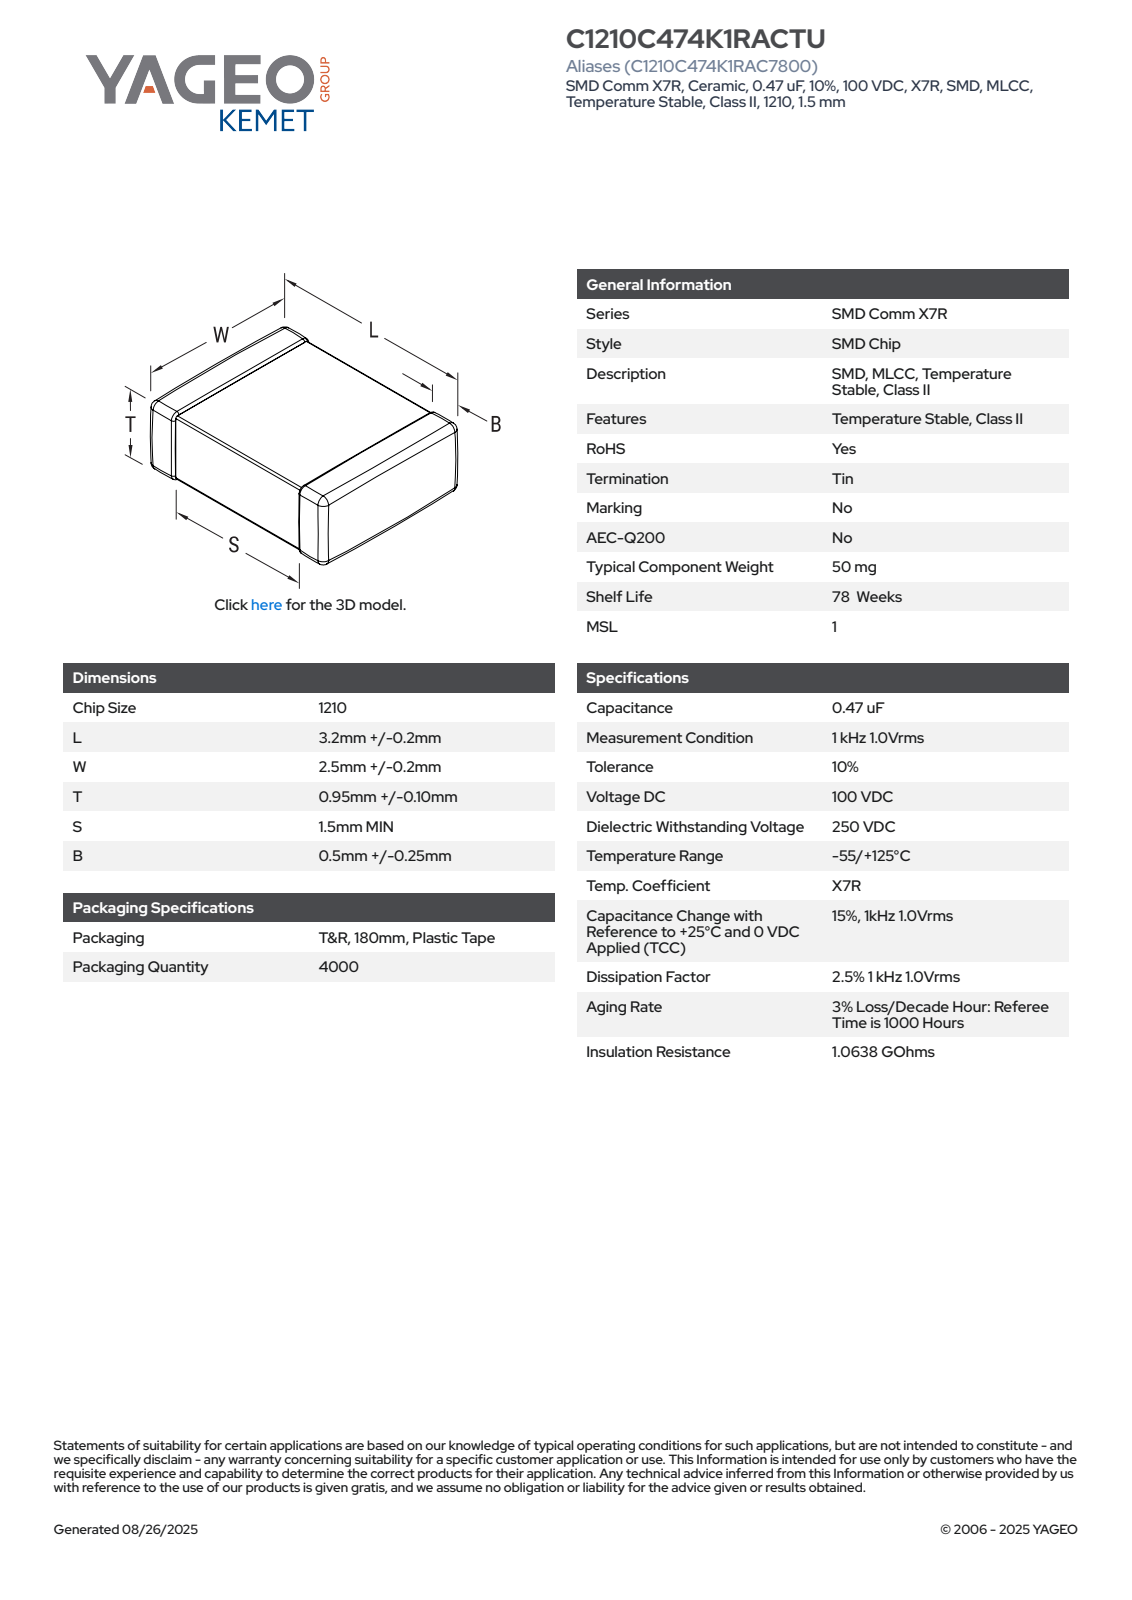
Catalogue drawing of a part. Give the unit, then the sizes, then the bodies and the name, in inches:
Units: inches
Overall size (bounding box): 0.197 × 0.065 × 0.045
Main face-to-face distances: 0.044, 0.043, 0.064, 0.063, 0.045, 0.065, 0.197, 0.097, 0.1, 0.106
Volume: 0.001 in³ · Surface area: 0.048 in²
Bodies: 4 solids, 125 faces (71 planar, 38 cylindrical, 16 other)
Part name (STEP PRODUCT): CCS_CCSTD_1210_L3.4W2.7T1.05B0.5
STEP written by: SolidWorks 2021 (AUTOMOTIVE_DESIGN)
